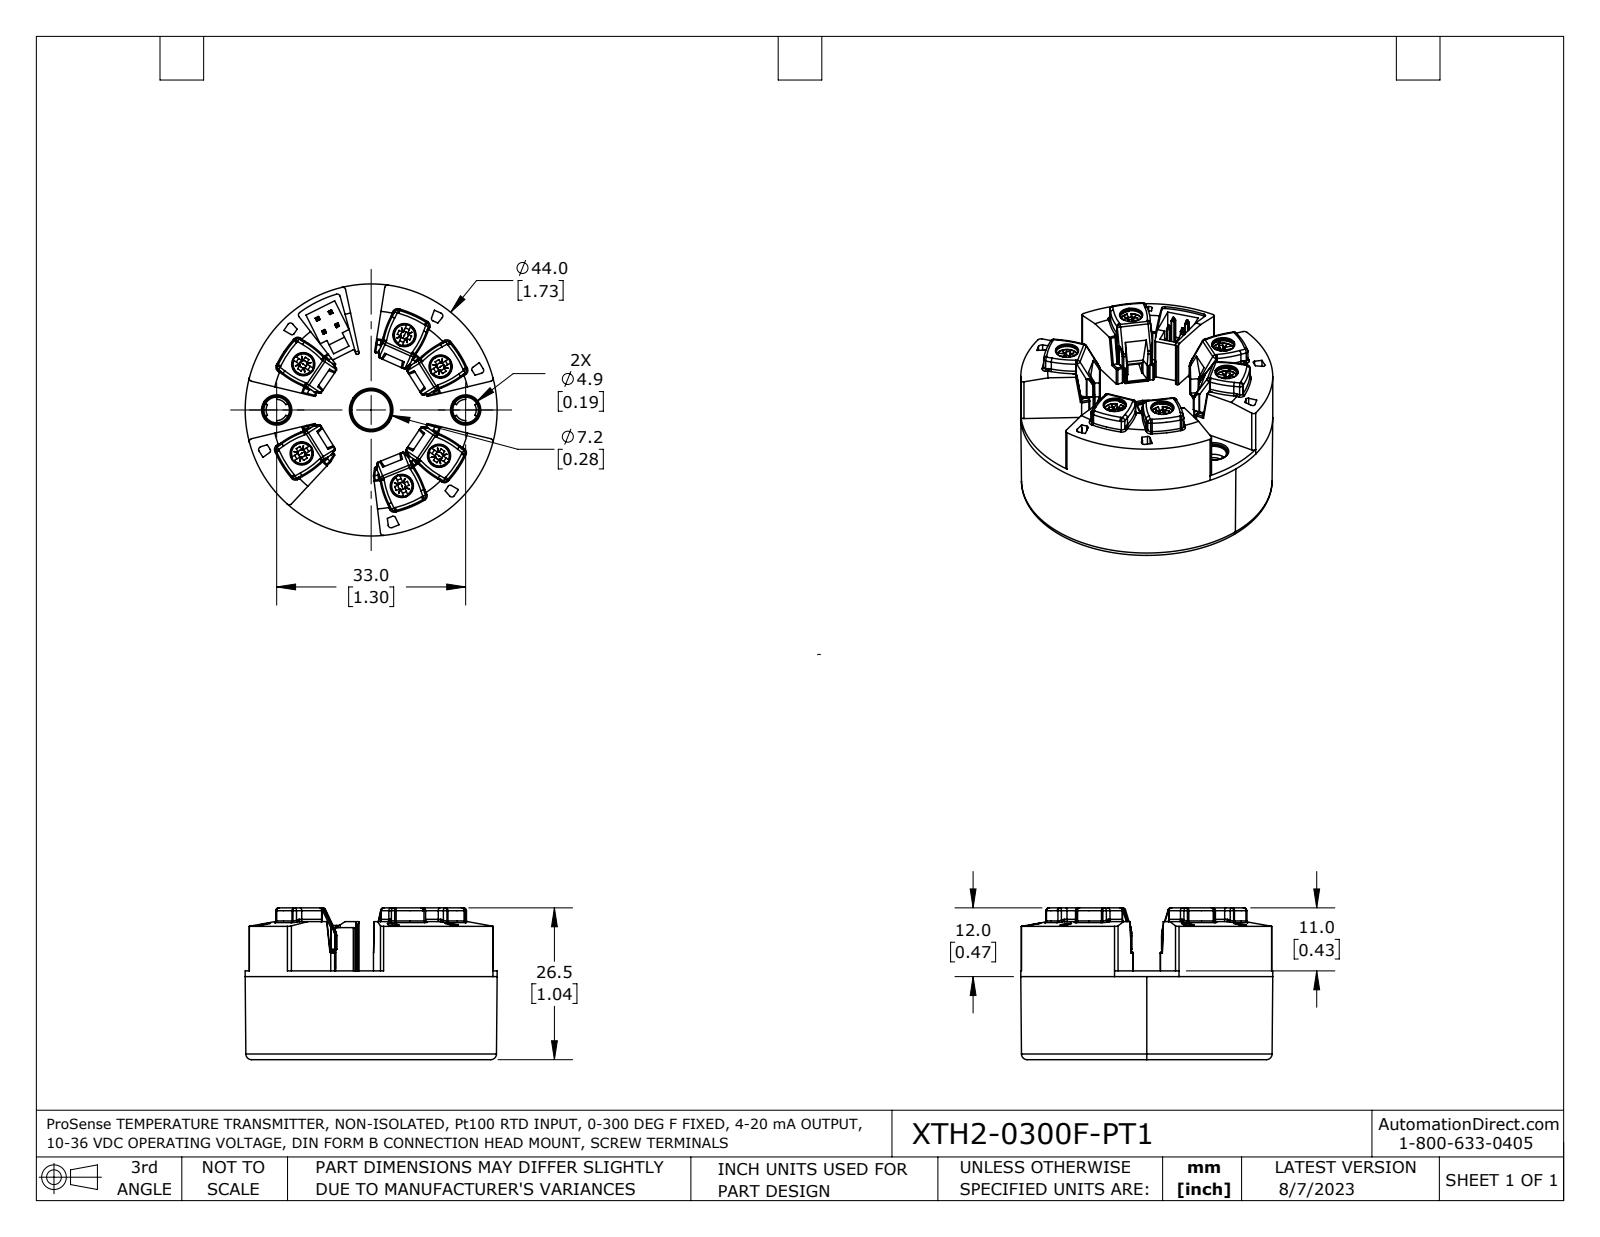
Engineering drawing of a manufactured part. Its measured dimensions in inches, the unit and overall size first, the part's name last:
Units: inches
Overall size (bounding box): 1.732 × 1.732 × 1.043
Round holes (diameter × count): ⌀0.102 ×6, ⌀0.151 ×6, ⌀0.159 ×6, ⌀0.193 ×2, ⌀0.248 ×2, ⌀0.213 ×1, ⌀0.283 ×1, ⌀0.339 ×1, ⌀0.685 ×1
Round bosses / shafts (diameter × count): ⌀0.106 ×12, ⌀0.156 ×6, ⌀0.098 ×6, ⌀1.732 ×1, ⌀1.646 ×1, ⌀0.402 ×1
Partial cylindrical surfaces — rounded edges, fillets, slot ends (radius × count): R0.008 ×247, R0.02 ×144, R0.012 ×58, R0.004 ×48, R0.01 ×36, R0.006 ×18, R0.016 ×12, R0.592 ×12
Main face-to-face distances: 0.039, 0.571, 0.453, 0.118, 0.492, 0.61, 0.079, 0.531, 0.098, 0.067
Hole centre spacings: 0.563, 0.863, 0.329, 0.344, 0.364, 0.563, 0.613, 0.65
Volume: 0.846 in³ · Surface area: 24.66 in²
Bodies: 1 solid, 2500 faces (944 planar, 967 cylindrical, 589 other)
Part name (STEP PRODUCT): XTH2-0300F-PT1
STEP written by: SolidWorks 2021 (AUTOMOTIVE_DESIGN)
